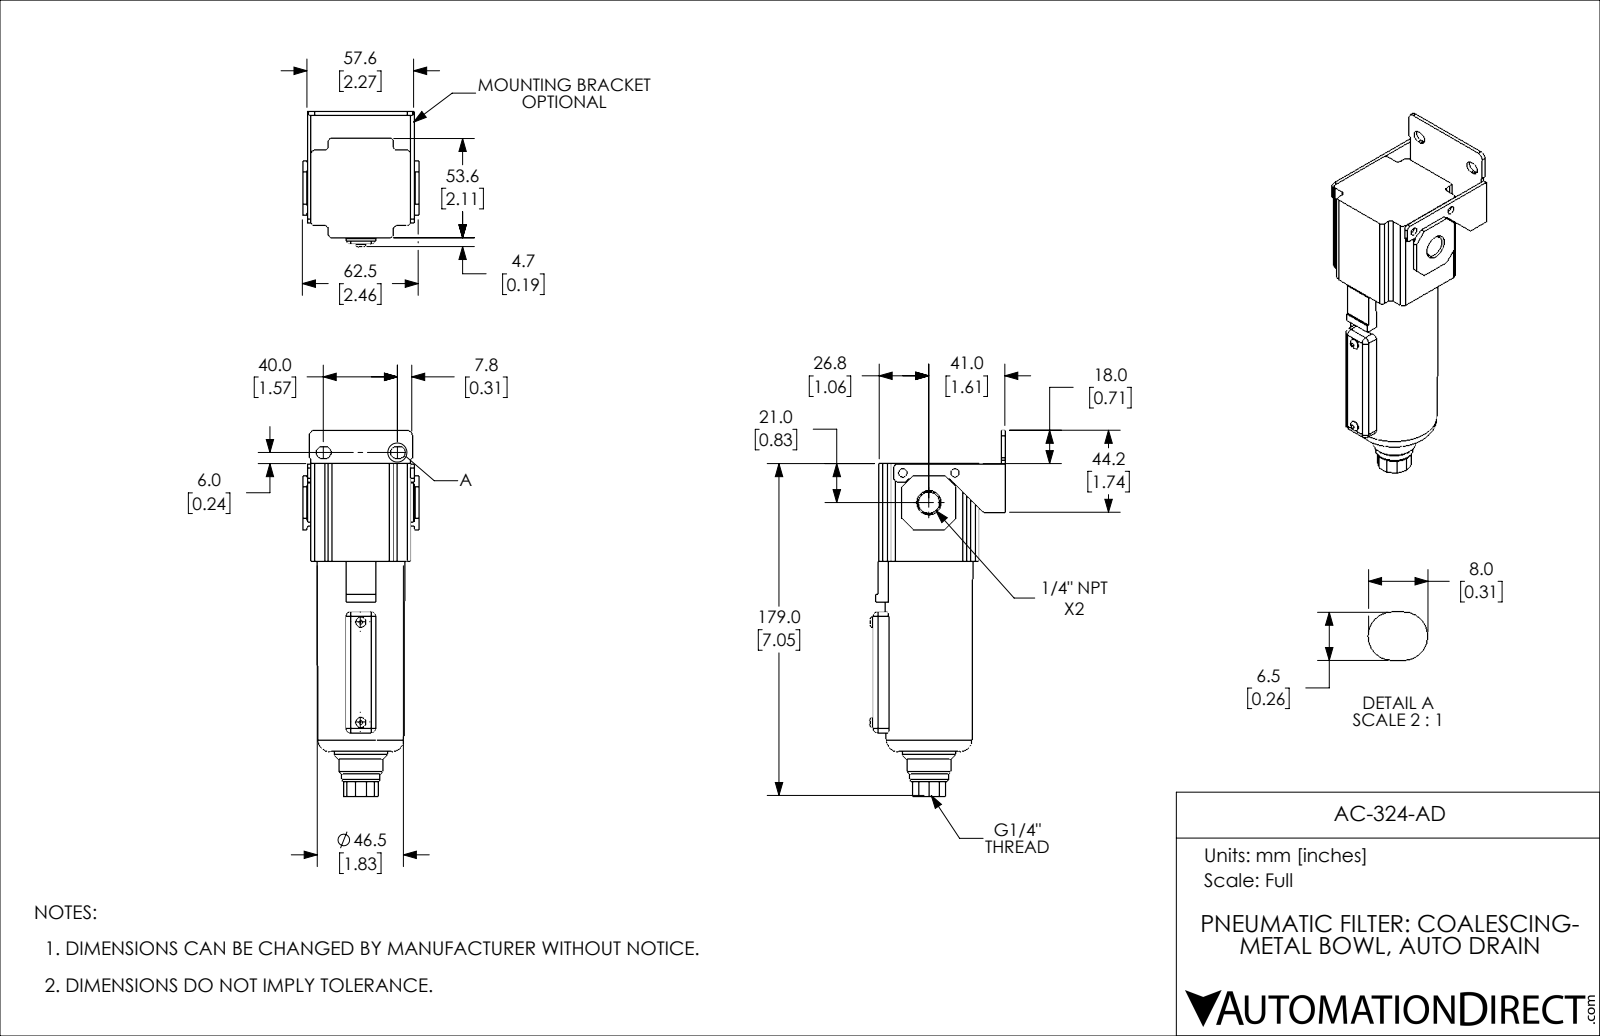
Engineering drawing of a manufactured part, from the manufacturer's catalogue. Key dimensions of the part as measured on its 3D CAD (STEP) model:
Part name (STEP PRODUCT): AC-324-AD
STEP written by: SolidWorks 2018 (AUTOMOTIVE_DESIGN)
Units: inches
Bodies: 1 solid, 200 faces (116 planar, 60 cylindrical, 24 other)
Overall size (bounding box): 7.756 × 2.854 × 2.461
Volume: 20.47 in³ · Surface area: 67.02 in²
Round holes (diameter × count): ⌀0.177 ×2, ⌀0.451 ×2
Round bosses / shafts (diameter × count): ⌀0.217 ×2, ⌀1.102 ×1, ⌀0.906 ×1, ⌀0.787 ×1
Partial cylindrical surfaces — rounded edges, fillets, slot ends (radius × count): R0.079 ×15, R0.098 ×8, R0.128 ×4, R0.039 ×2, R0.118 ×2
Main face-to-face distances: 0.079, 2.11, 2.189, 0.559, 2.669, 0.48, 2.591, 0.096, 0.175, 2.285
Hole centre spacings: 0.837, 1.102
